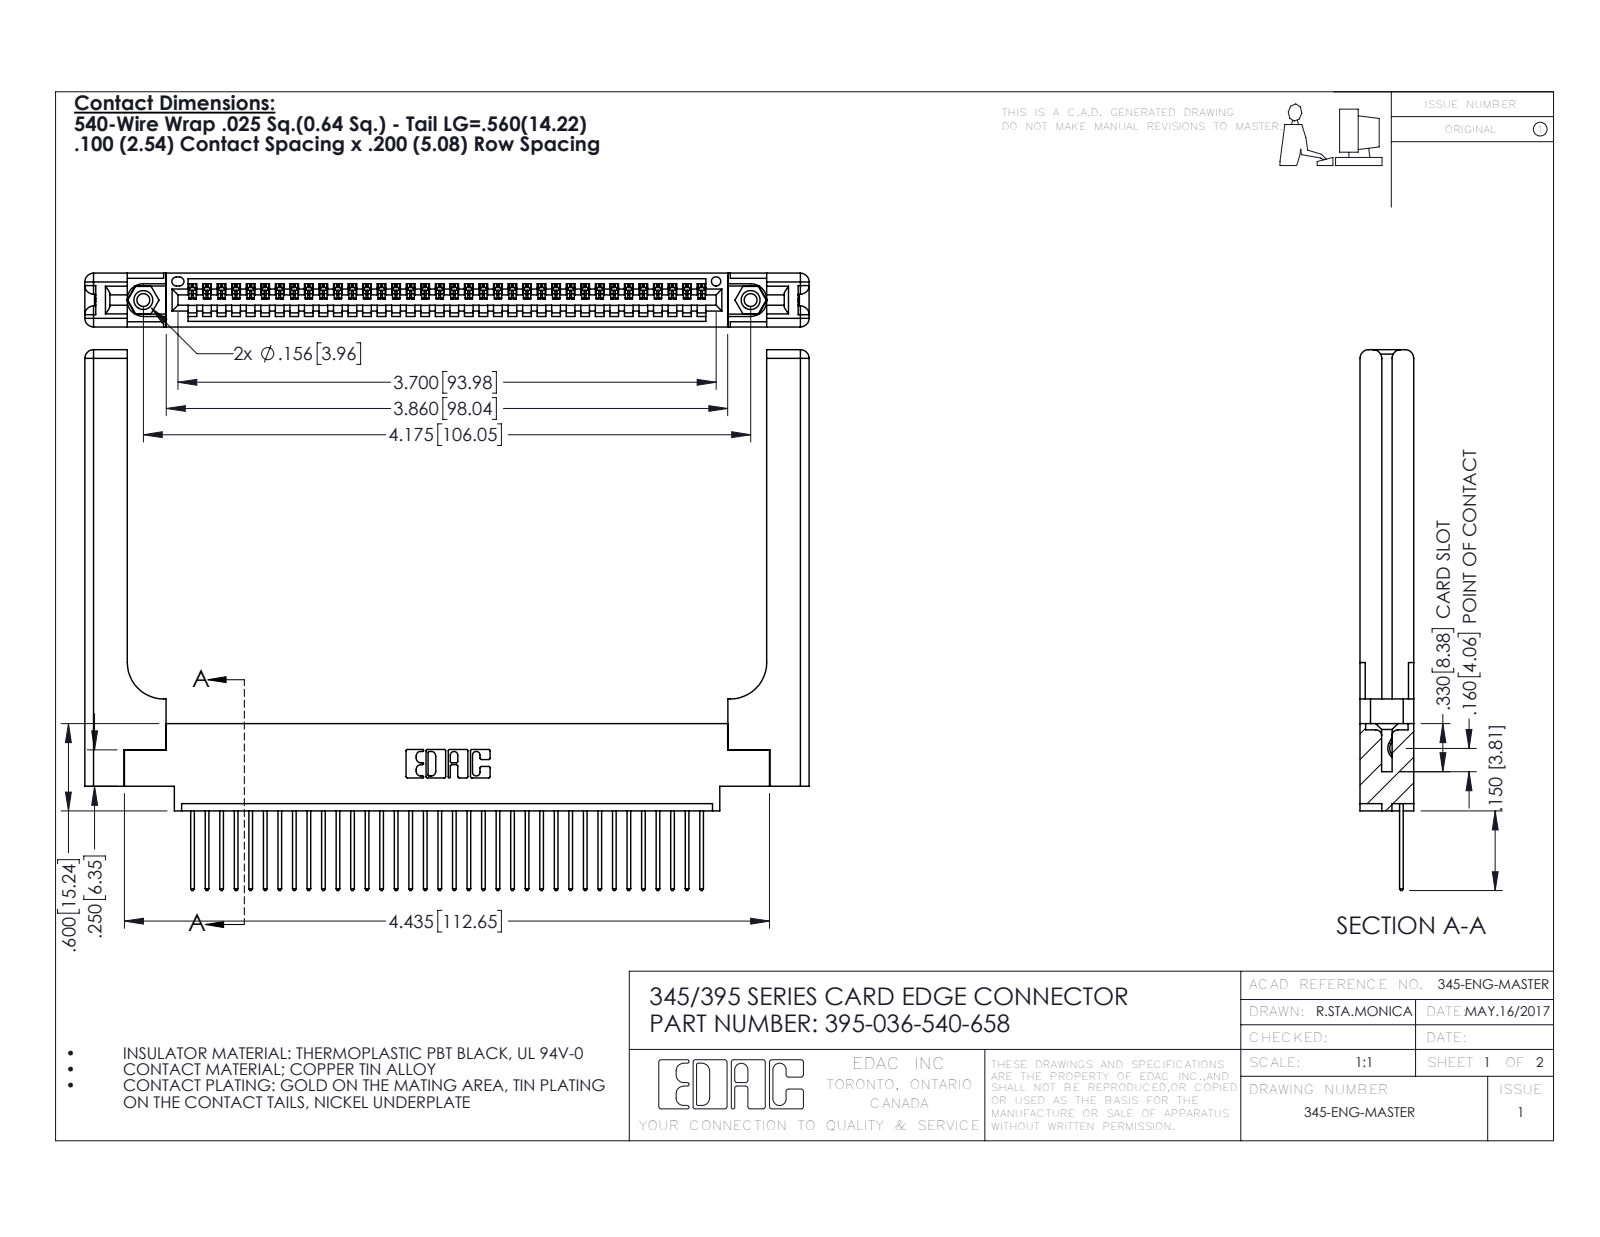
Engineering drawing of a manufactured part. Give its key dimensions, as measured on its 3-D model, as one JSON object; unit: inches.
{"part_name": "345-220-058_345-220-058; 345-250-001_345-250-001-102; 395-036-540-658; 345 Part_0.170 Offset - 0.156 Dia-TH (+1 more)", "step_written_by": "SolidWorks 2016 (CONFIG_CONTROL_DESIGN)", "units": "inches", "bodies": {"solids": 41, "faces": 2474, "planar": 1672, "cylindrical": 742, "other": 60}, "overall_size": [4.979, 3.717, 0.37], "volume_in3": 1.245, "surface_area_in2": 33.35, "round_holes": [[0.089, 2], [0.125, 2], [0.156, 2], [0.064, 1]], "round_bosses_or_shafts": [[0.155, 2]], "partial_cylinders_radius": [[0.006, 72], [0.01, 72], [0.01, 22], [0.06, 16], [0.007, 6], [0.031, 6], [0.026, 3], [0.03, 2]], "face_to_face_distances": [0.37, 0.072, 0.298, 0.098, 0.272, 0.025, 0.2, 0.148, 0.15, 0.225], "hole_center_spacings": [0.27, 3.939, 4.175]}
